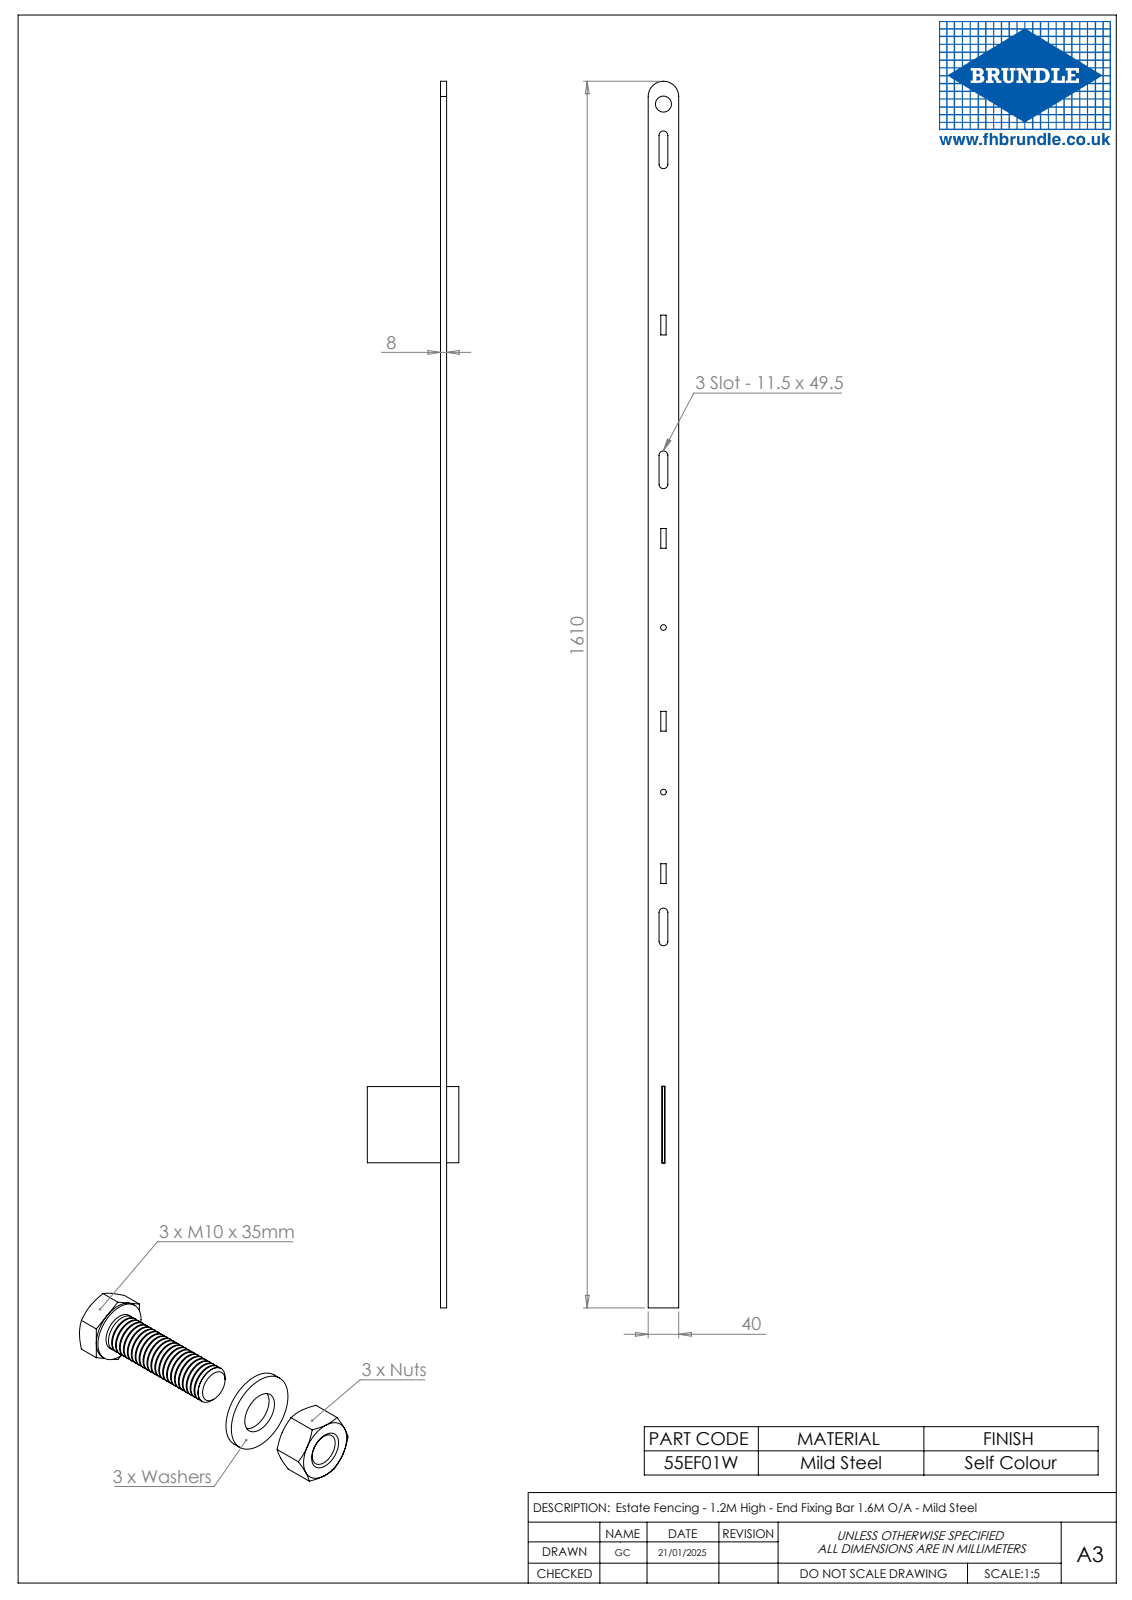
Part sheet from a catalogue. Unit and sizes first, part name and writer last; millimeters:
Units: millimetres
Overall size (bounding box): 1610 × 120 × 40
Round holes (diameter × count): ⌀7.5 ×2, ⌀21 ×1
Partial cylindrical surfaces — rounded edges, fillets, slot ends (radius × count): R5.75 ×6, R20 ×1
Main face-to-face distances: 8, 18.5, 21.5, 40, 3, 14.25, 25.75, 4.25, 7.25, 0.5
Hole centre spacings: 216, 687, 903
Volume: 524 312 mm³ · Surface area: 181 048 mm²
Bodies: 2 solids, 51 faces (37 planar, 14 cylindrical, 0 other)
Part name (STEP PRODUCT): 0149-010-02_fixed panel_end bar; 0149-020-16_end fixing bar trust plate; 55EF01
STEP written by: SolidWorks 2023 (CONFIG_CONTROL_DESIGN)
